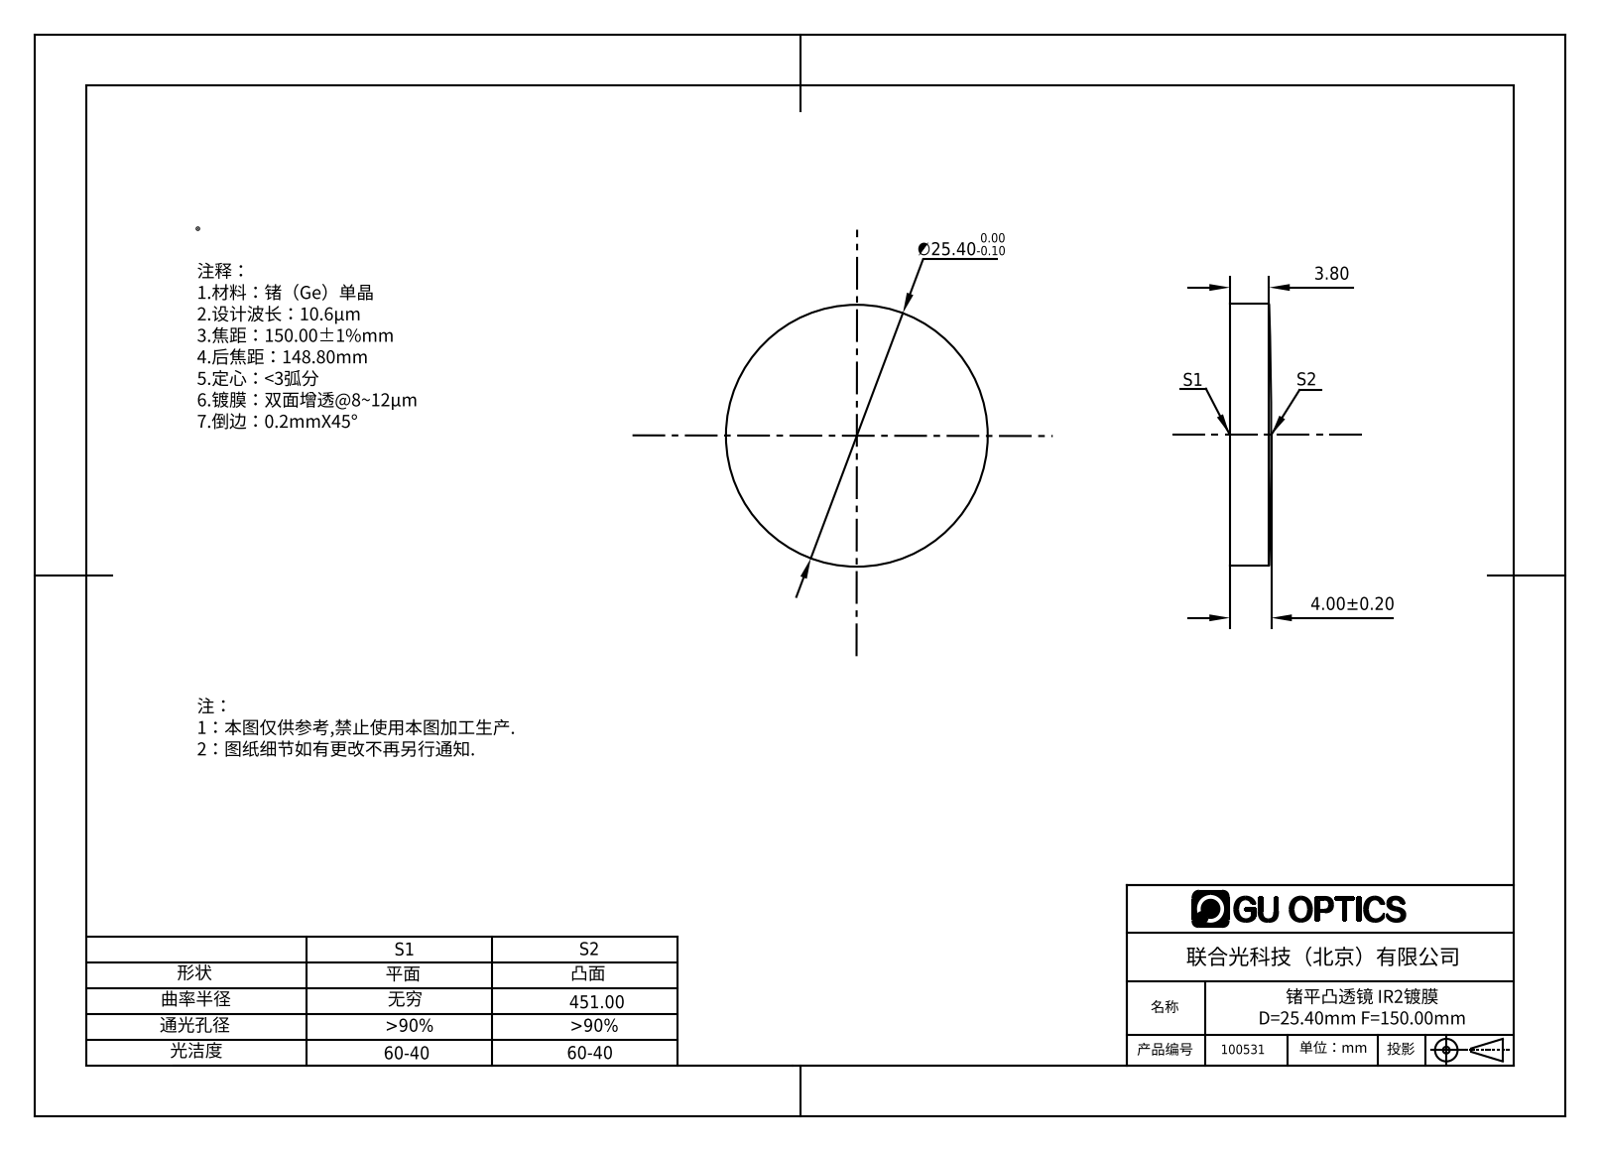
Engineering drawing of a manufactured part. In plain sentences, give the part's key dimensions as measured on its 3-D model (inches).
The part is named "100519". Its 3-D file was written by "SolidWorks 2016 (AUTOMOTIVE_DESIGN)". It is 1 solid with 5 faces: 1 planar, 2 cylindrical and 2 other. Overall it measures 1 by 1 by 0.157 inches. Its volume is 0.121 cubic inches and its surface area 2.041 square inches. Round bosses or shafts: 1 of diameter 1.
